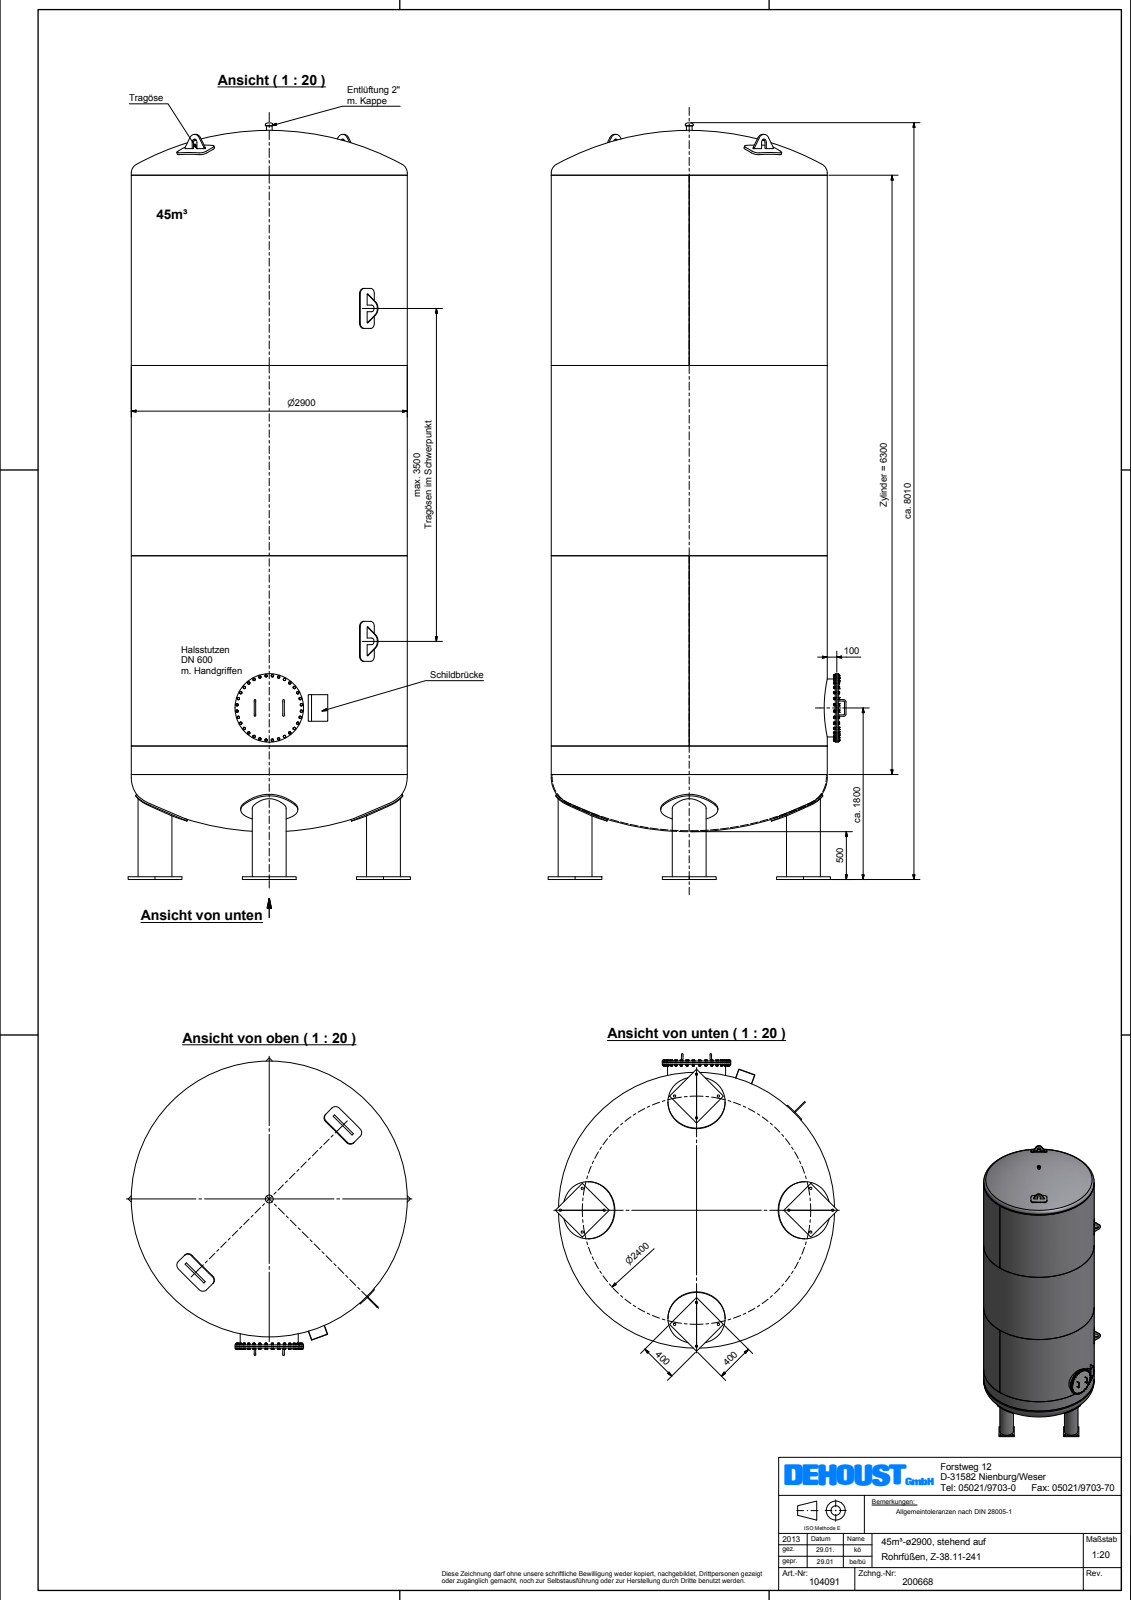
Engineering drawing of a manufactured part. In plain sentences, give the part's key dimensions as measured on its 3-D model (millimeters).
The part is named "Beh\\S\\dlter_Z-38_11-241_2900_045_KV". Its 3-D file was written by "Autodesk Inventor 2012 (AUTOMOTIVE_DESIGN)". It is 9 solids with 1130 faces: 636 planar, 166 cylindrical and 328 other. Overall it measures 7957.07 by 3129.84 by 2965.68 millimeters. Its volume is 3 167 000 000 cubic millimeters and its surface area 157 600 000 square millimeters. Round holes: 4 of diameter 230, 4 of diameter 336.6, 1 of diameter 598, 1 of diameter 2880, 1 of diameter 2886, 1 of diameter 2888. Round bosses or shafts: 38 of diameter 16, 32 of diameter 22.5, 4 of diameter 600, 4 of diameter 355.6, 1 of diameter 2900, 1 of diameter 720, 1 of diameter 660, 1 of diameter 610. Partial cylindrical surfaces (rounded edges, fillets, slot ends): 16 of radius 56, 4 of radius 35, 4 of radius 85, 1 of radius 1460. The main face-to-face distances are 1104.11, 30, 1074.11, 35, 16, 19, 3.02, 399.94, 1696.8, 10. The hole center spacings are 1200, 1697.06, 2400.
